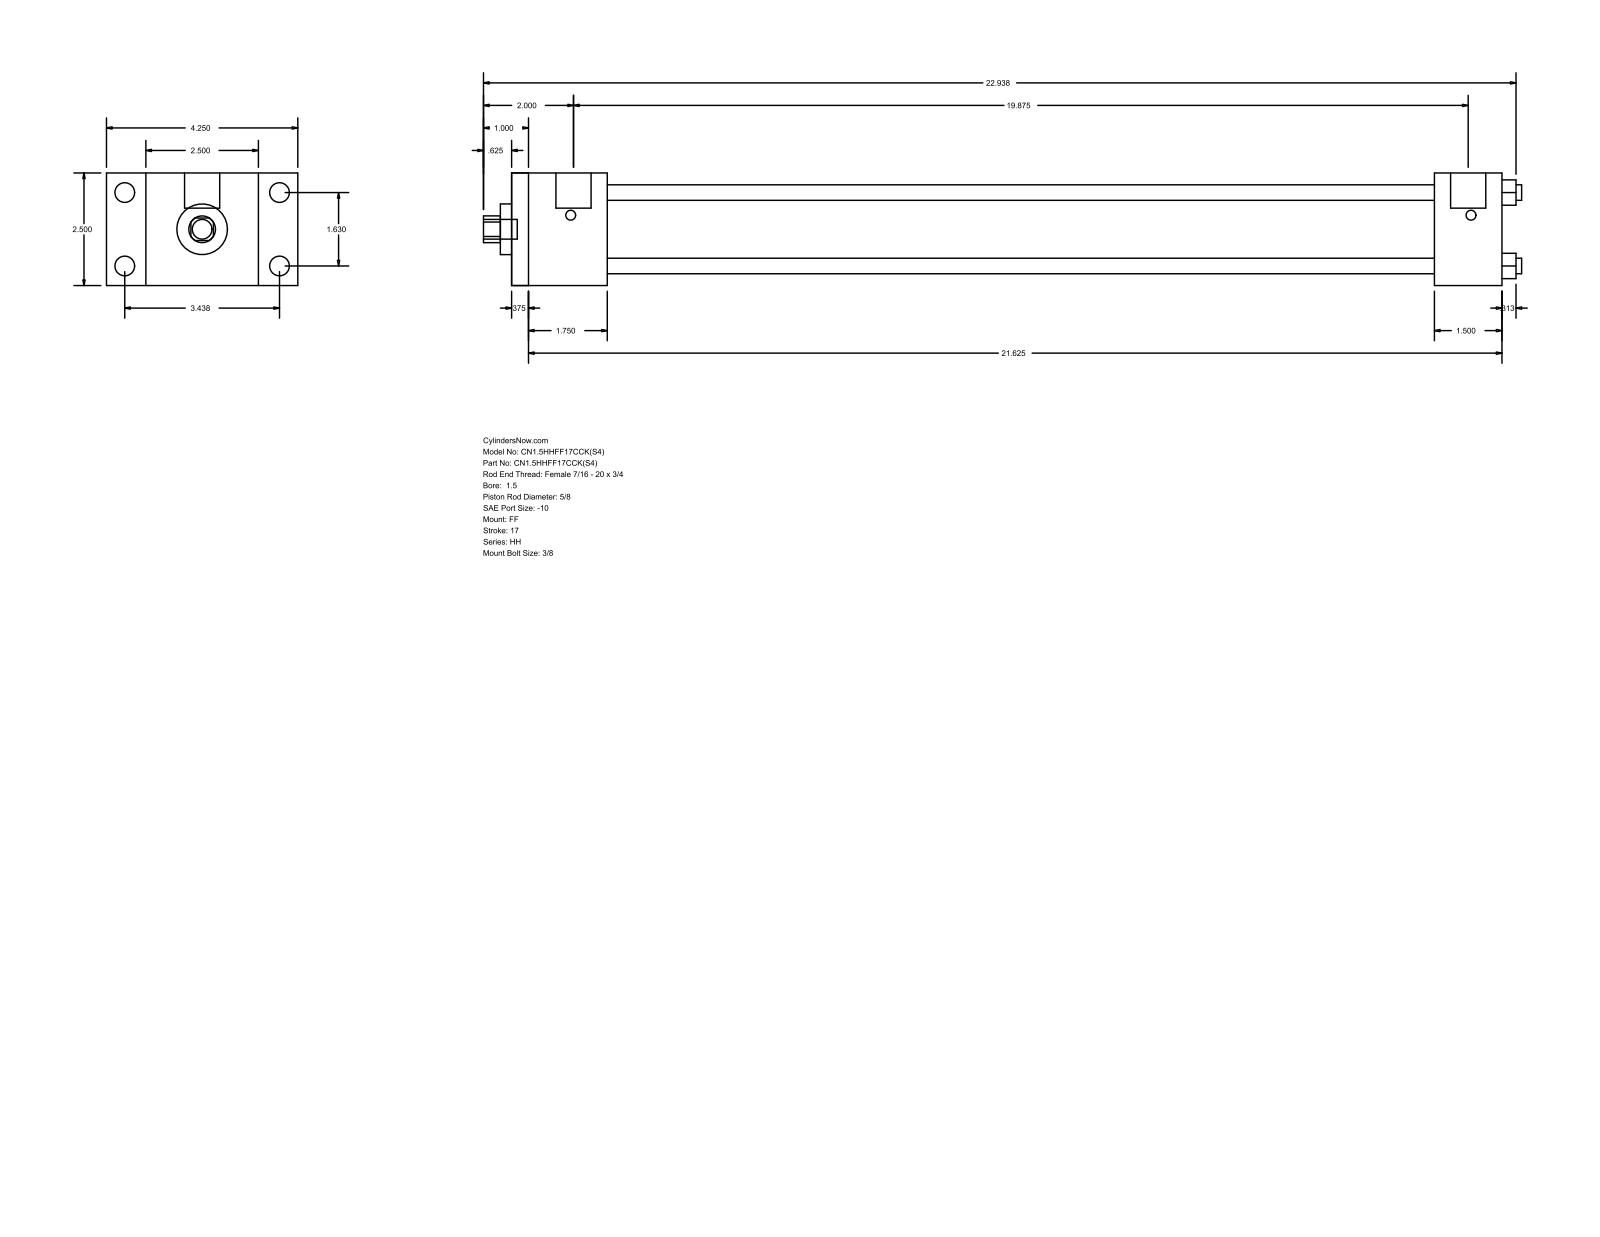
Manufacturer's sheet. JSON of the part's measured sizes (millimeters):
{"part_name": "HH_FF__0150_0.625", "step_written_by": "GSSL Pune (CONFIG_CONTROL_DESIGN)", "units": "millimeters", "bodies": {"solids": 0, "faces": 92, "planar": 64, "cylindrical": 28, "other": 0}, "overall_size": [585.79, 107.95, 63.5], "round_holes": [[8.76, 4], [15.88, 1], [28.57, 1], [44.45, 1]], "round_bosses_or_shafts": [[11.13, 4], [5.56, 4], [19.84, 2], [11.11, 1]], "partial_cylinders_radius": [[7.54, 1]], "face_to_face_distances": [63.5, 558.79, 9.52, 549.27, 53.97, 44.45, 504.82, 520.7, 511.18, 466.73], "hole_center_spacings": [29.27, 41.4, 58.55]}
